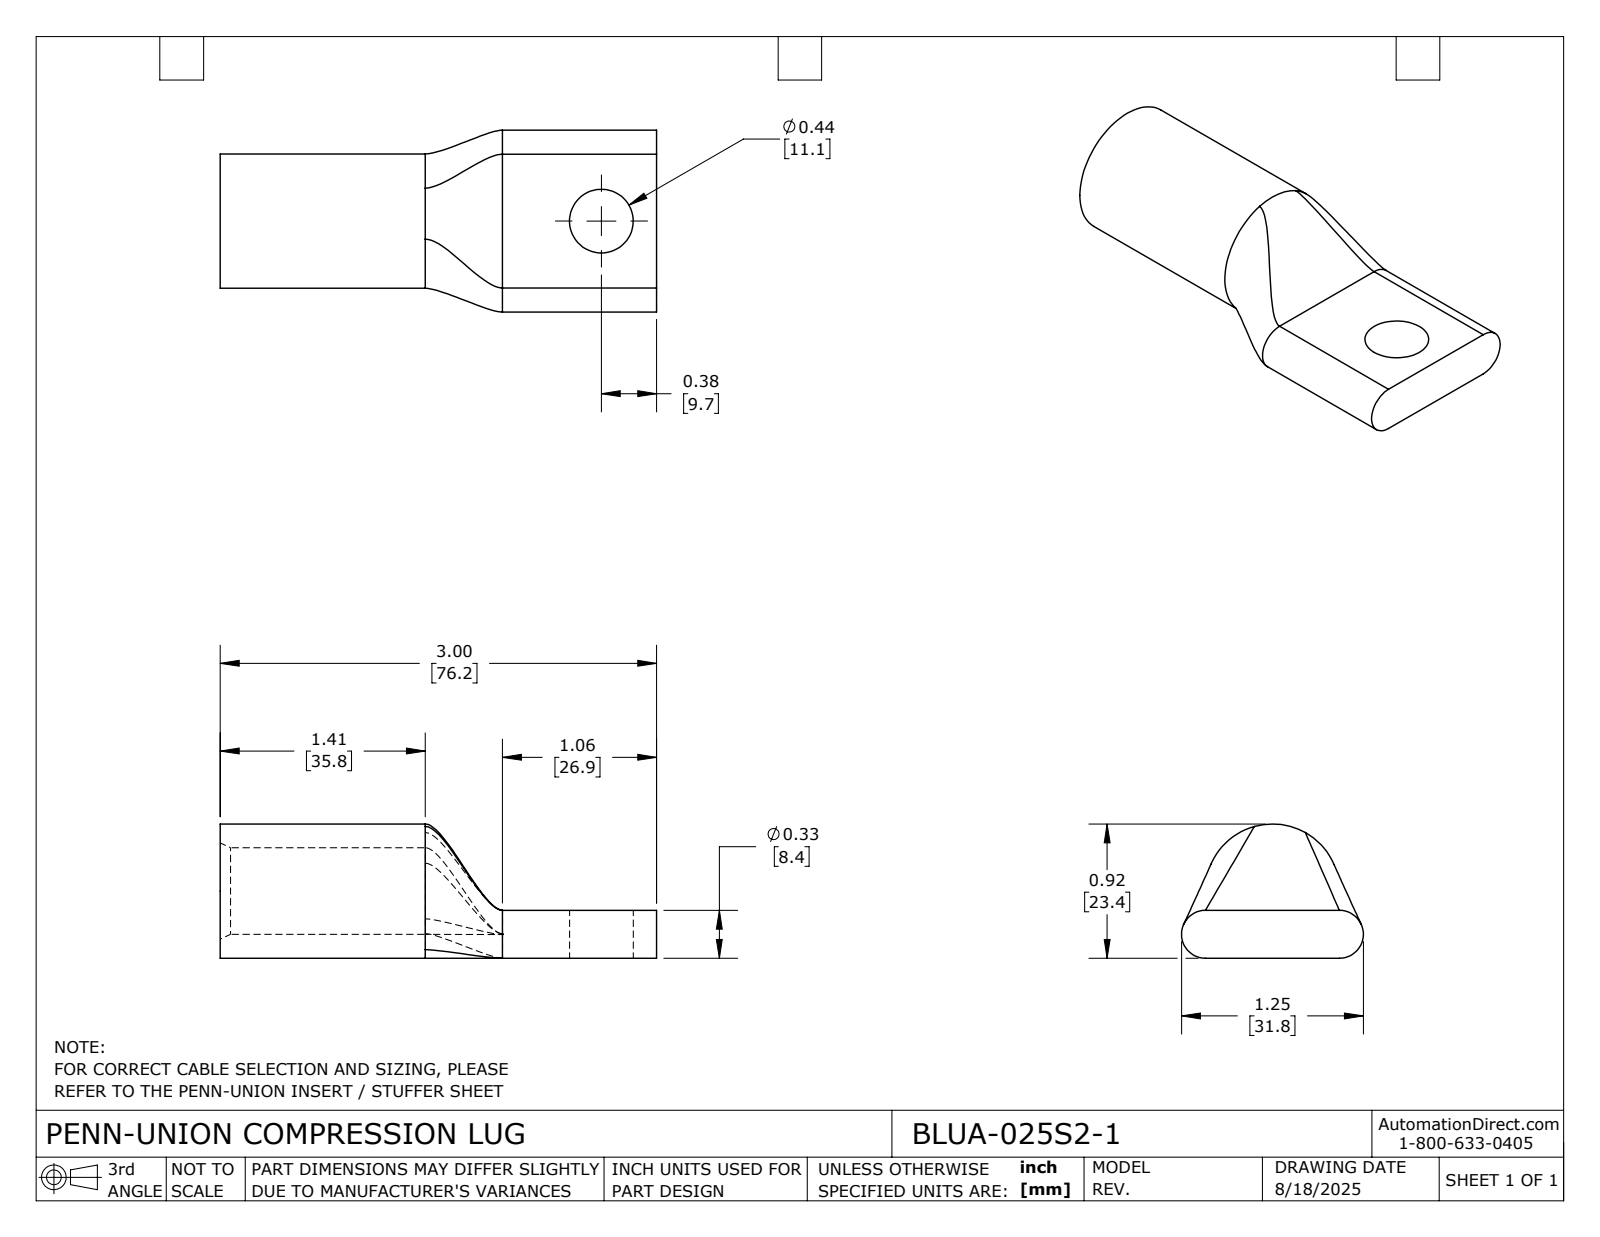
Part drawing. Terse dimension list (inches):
name: BLUA-025S2-1
written by: SolidWorks 2024 (CONFIG_CONTROL_DESIGN)
unit: in
bodies: 1 solid, 24 faces (5 planar, 9 cylindrical, 10 other)
size: 3 × 1.25 × 0.923
volume: 1.117 in³; area: 13.58 in²
holes: 1× ⌀0.438, 1× ⌀0.595
bosses: 1× ⌀0.923
rounds: 2× R0.165
face distances: 0.33, 3, 1.94, 1.06
